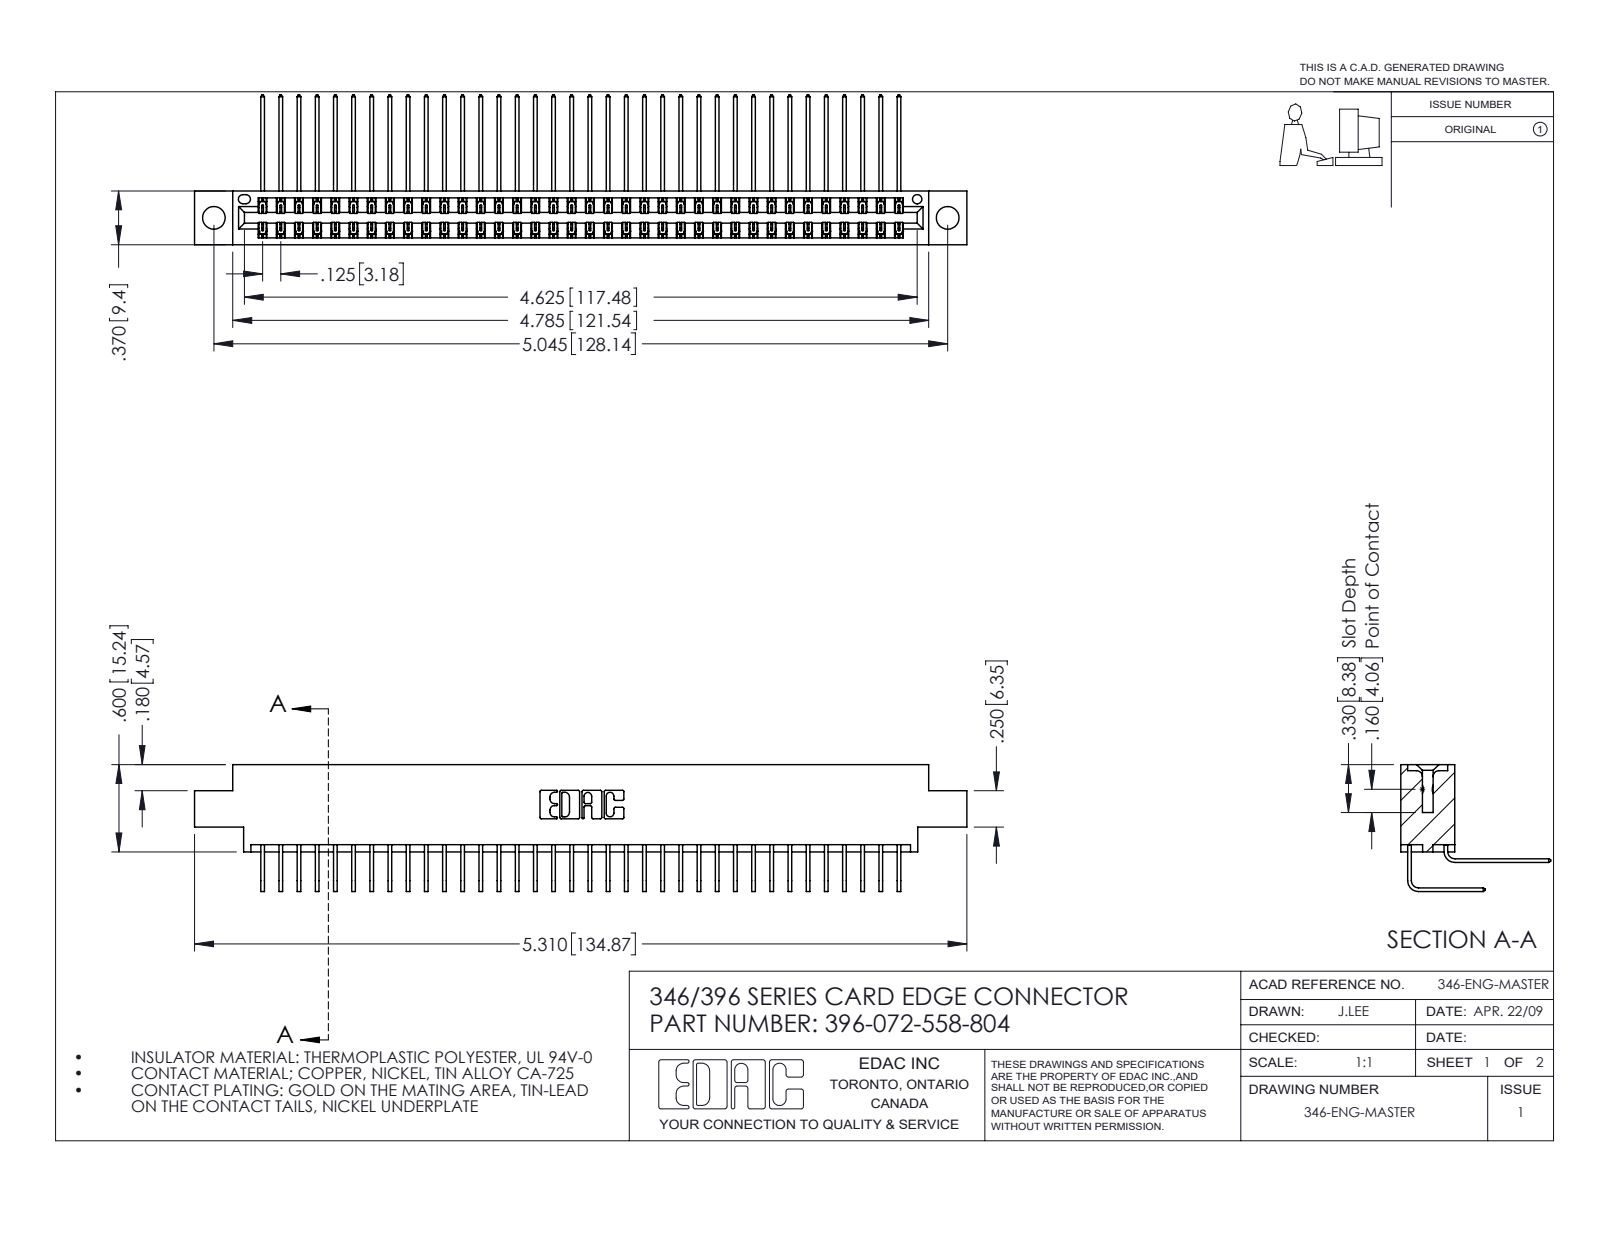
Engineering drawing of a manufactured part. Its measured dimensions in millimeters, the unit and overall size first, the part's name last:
Units: millimetres
Overall size (bounding box): 134.9 × 26.2 × 22.2
Round holes (diameter × count): ⌀4 ×2, ⌀1.6 ×1
Partial cylindrical surfaces — rounded edges, fillets, slot ends (radius × count): R0.2 ×108, R0.3 ×22, R0.2 ×6, R0.8 ×6, R0.7 ×3, R0.4 ×2, R0.6 ×2, R0.6 ×2
Main face-to-face distances: 8.2, 1.2, 0.6, 9.4, 6.4, 7.6, 1.8, 7, 3.8, 5.6
Hole centre spacings: 6.2, 122.8, 128.1
Volume: 13 300 mm³ · Surface area: 20 140 mm²
Bodies: 73 solids, 4014 faces (2744 planar, 1270 cylindrical, 0 other)
Part name (STEP PRODUCT): 345-292-001_558 Tail - 2; 396-072-558-804; 345-292-001_558 559 Tail - 1; 346 Part_0.170 Offset - 0.156 Dia-TH
STEP written by: SolidWorks 2016 (CONFIG_CONTROL_DESIGN)
